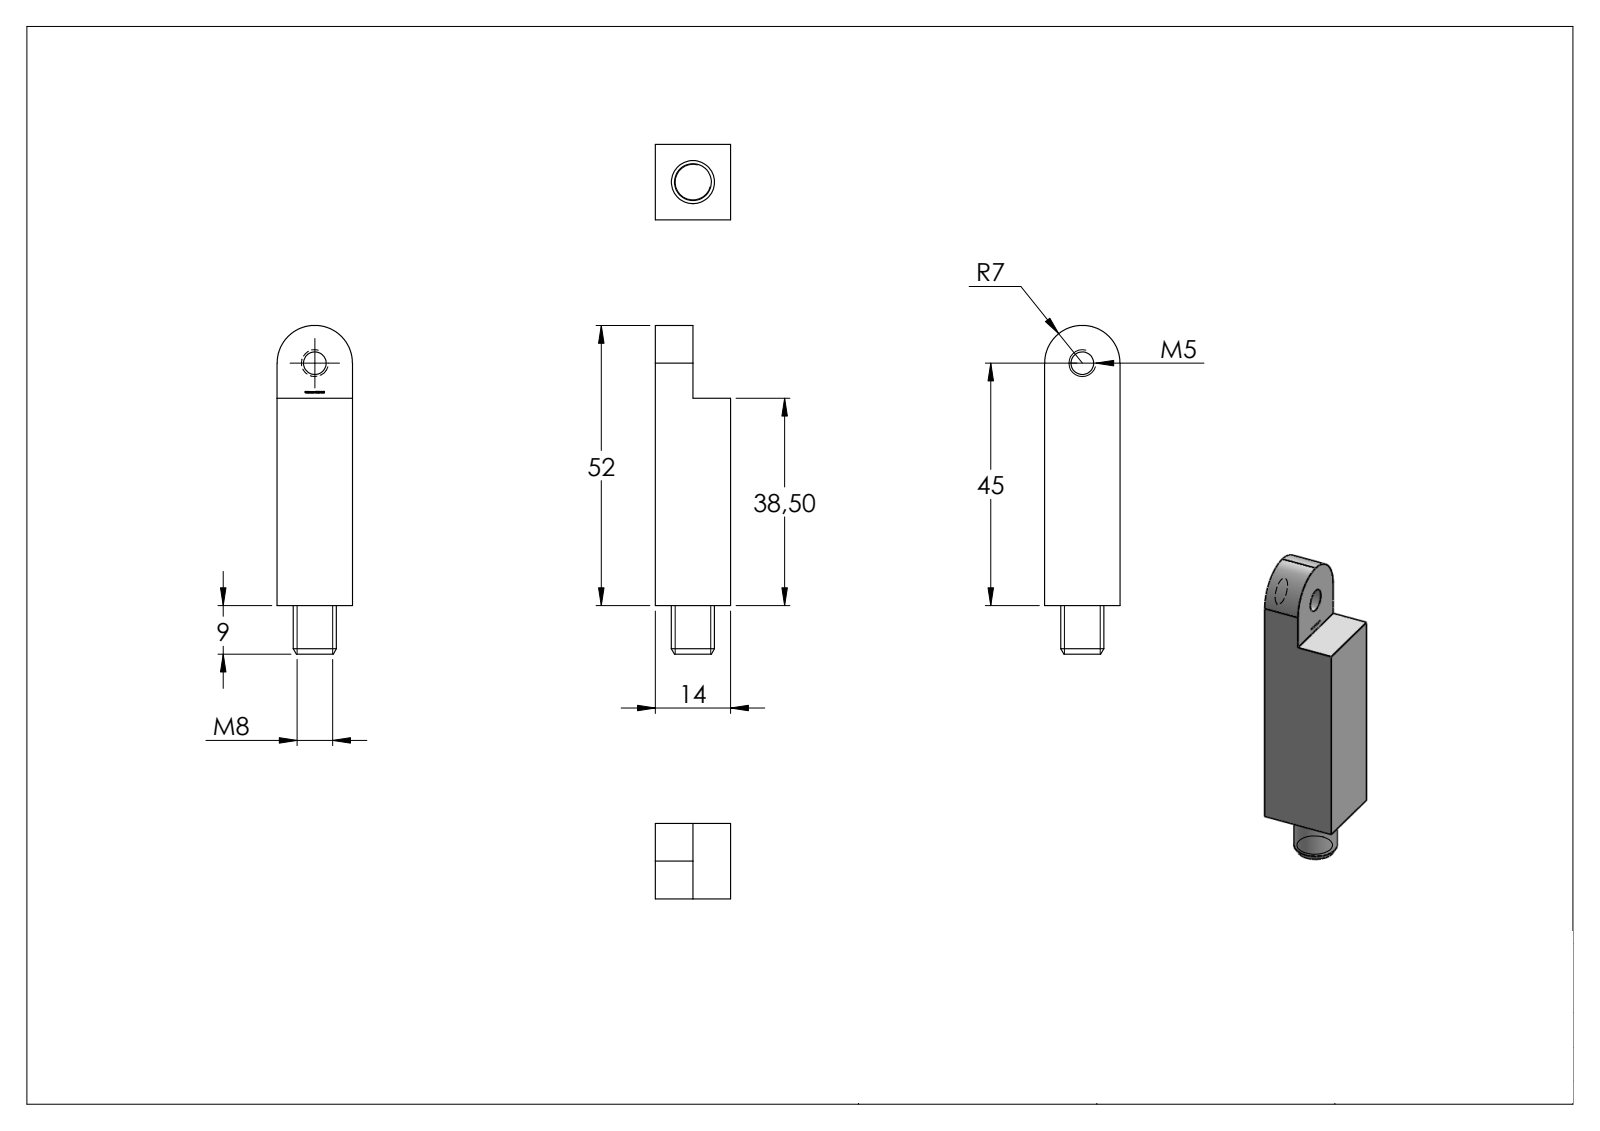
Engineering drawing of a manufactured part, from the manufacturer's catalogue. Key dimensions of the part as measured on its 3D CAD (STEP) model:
Part name (STEP PRODUCT): ISO7380_Rundkopfschraube mit Innensechskant_-_M5x8_M5x8; 60226-240 Teil1; 60226-240; 60226-240 Teil2
STEP written by: SolidWorks 2015 (CONFIG_CONTROL_DESIGN)
Units: millimetres
Bodies: 3 solids, 285 faces (146 planar, 18 cylindrical, 121 other)
Overall size (bounding box): 77 × 14 × 14
Volume: 12 780 mm³ · Surface area: 5 665 mm²
Round holes (diameter × count): ⌀4.2 ×1, ⌀5 ×1, ⌀5.5 ×1, ⌀10.2 ×1
Round bosses / shafts (diameter × count): ⌀10 ×1, ⌀8 ×1, ⌀4.02 ×1
Partial cylindrical surfaces — rounded edges, fillets, slot ends (radius × count): R7 ×2
Main face-to-face distances: 14, 7, 3.5, 10.5, 38.5, 52.25, 13.75, 68, 29.5, 15.75
